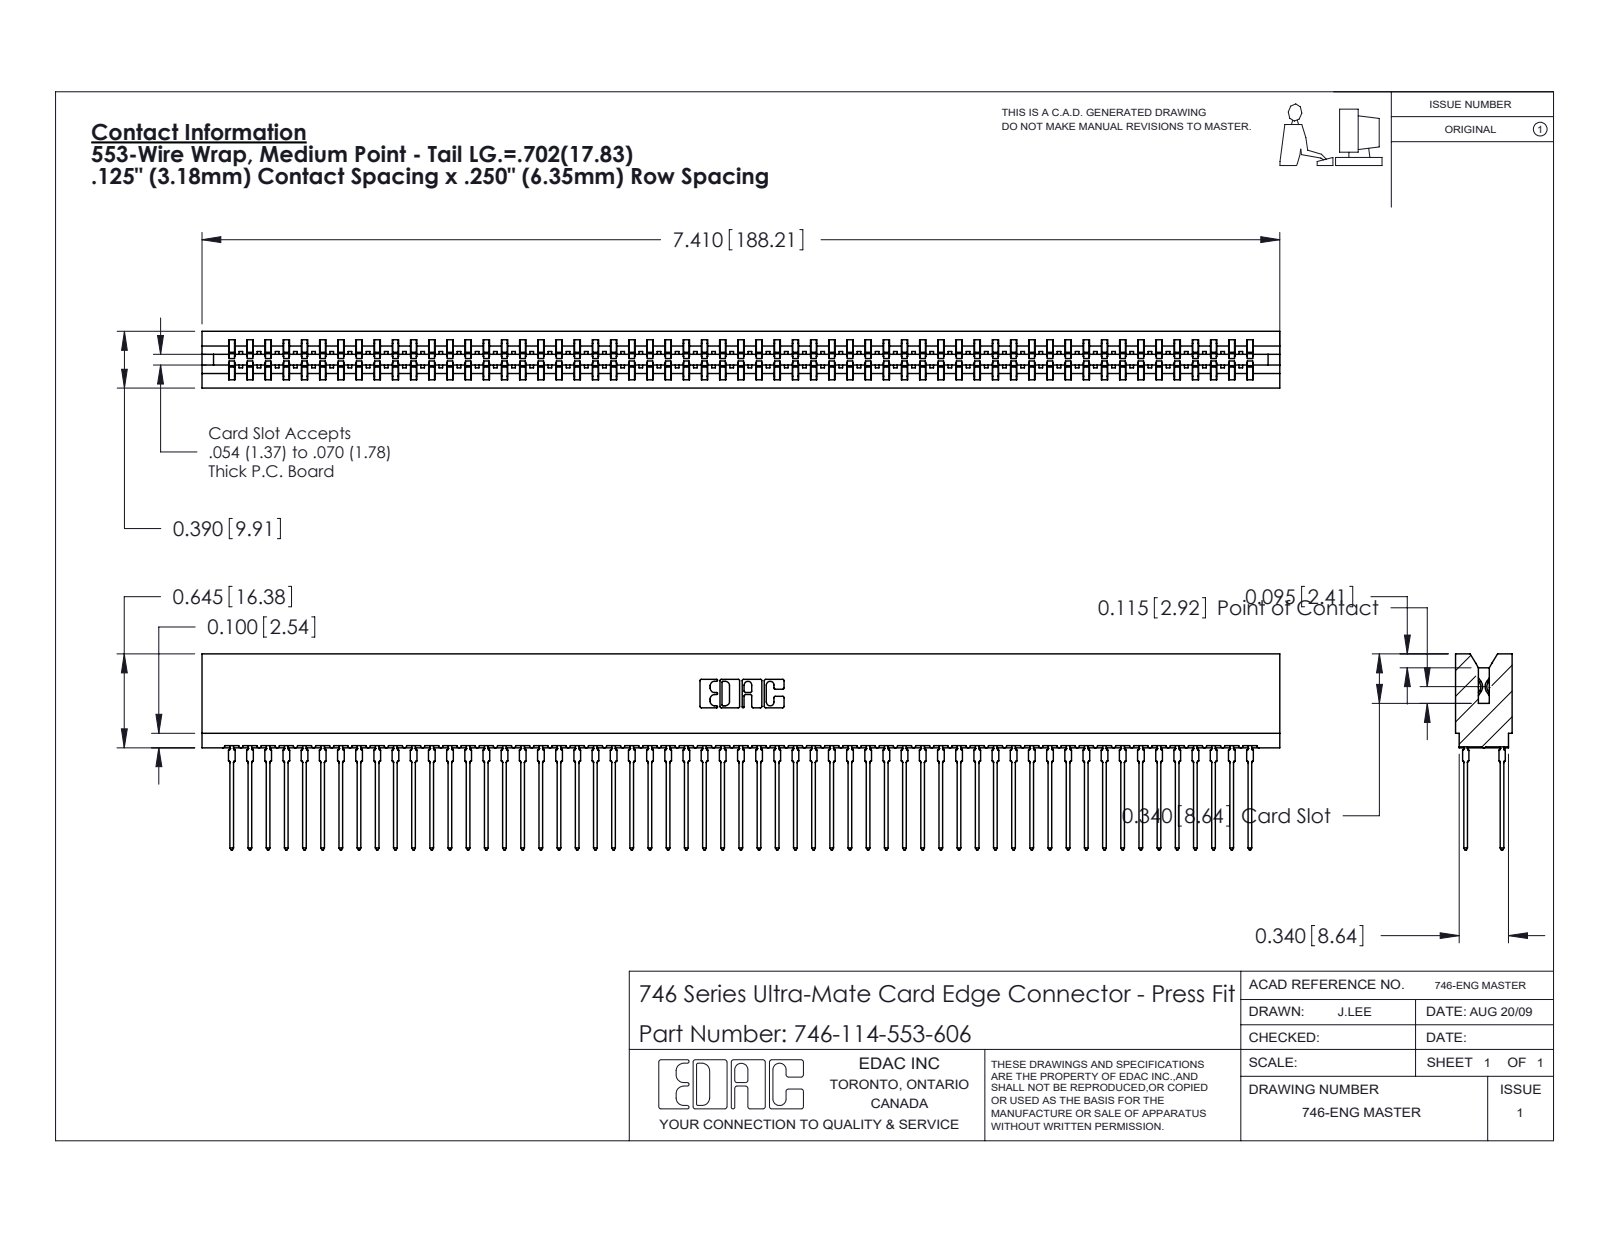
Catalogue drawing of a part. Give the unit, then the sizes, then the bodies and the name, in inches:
Units: inches
Overall size (bounding box): 7.41 × 1.346 × 0.39
Partial cylindrical surfaces — rounded edges, fillets, slot ends (radius × count): R0.021 ×228, R0.015 ×58, R0.01 ×22, R0.005 ×8, R0.011 ×8, R0.007 ×6, R0.031 ×6, R0.026 ×3
Main face-to-face distances: 0.057, 0.333, 0.025, 0.307, 0.25, 0.39, 0.083, 0.275, 0.225, 0.015
Volume: 1.346 in³ · Surface area: 54.23 in²
Bodies: 115 solids, 10301 faces (5300 planar, 2037 cylindrical, 2964 other)
Part name (STEP PRODUCT): 746 Part_.340 Slot Depth - 06; 746-292-001_553; 746-114-553-606
STEP written by: SolidWorks 2020 (CONFIG_CONTROL_DESIGN)
